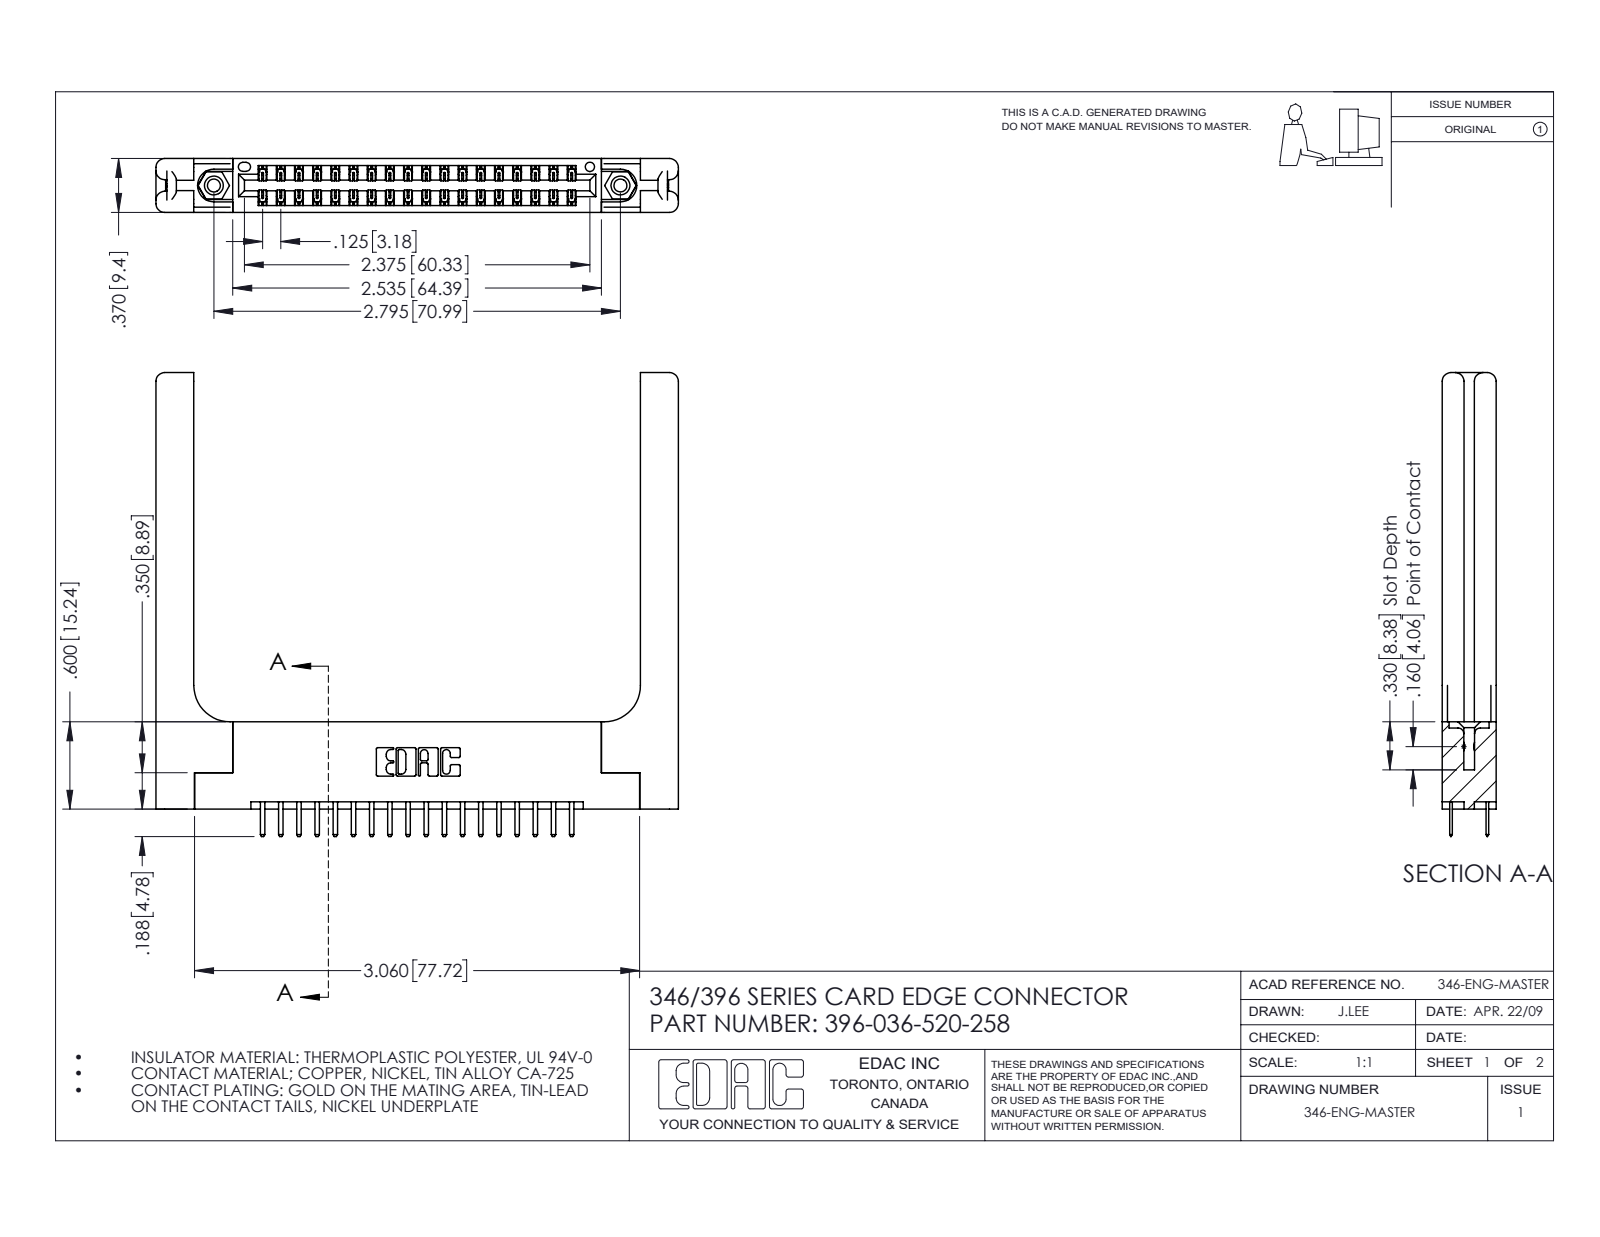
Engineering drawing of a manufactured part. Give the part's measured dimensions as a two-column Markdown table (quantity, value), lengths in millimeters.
| quantity | value |
| --- | --- |
| part name | 345-250-001_345-250-001-102; 346 Part_Flush Mounting Lugs - 0.156 Dia-TH; 346-220-058_345-220-058; 396-036-520-258 (+1 more) |
| STEP written by | SolidWorks 2016 (CONFIG_CONTROL_DESIGN) |
| units | millimeters |
| bodies | 41 solids, 2394 faces (1556 planar, 778 cylindrical, 60 other) |
| overall size | 91.2 × 81 × 9.4 |
| volume | 16 200 mm³ |
| surface area | 16 500 mm² |
| round holes (diameter × count) | 2.3 × 2, 3.2 × 2, 4 × 2, 1.6 × 1 |
| round bosses / shafts (diameter × count) | 3.9 × 2 |
| partial cylindrical surfaces (radius × count) | 0.2 × 54, 0.3 × 40, 0.3 × 22, 1.5 × 16, 0.2 × 6, 0.8 × 6, 0.7 × 3, 0.4 × 2 |
| main face-to-face distances | 9.4, 3.8, 1.8, 3.8, 1.2, 8.2, 6.4, 2.6, 5.6, 4.4 |
| hole center spacings | 6.2, 65.7, 71 |
